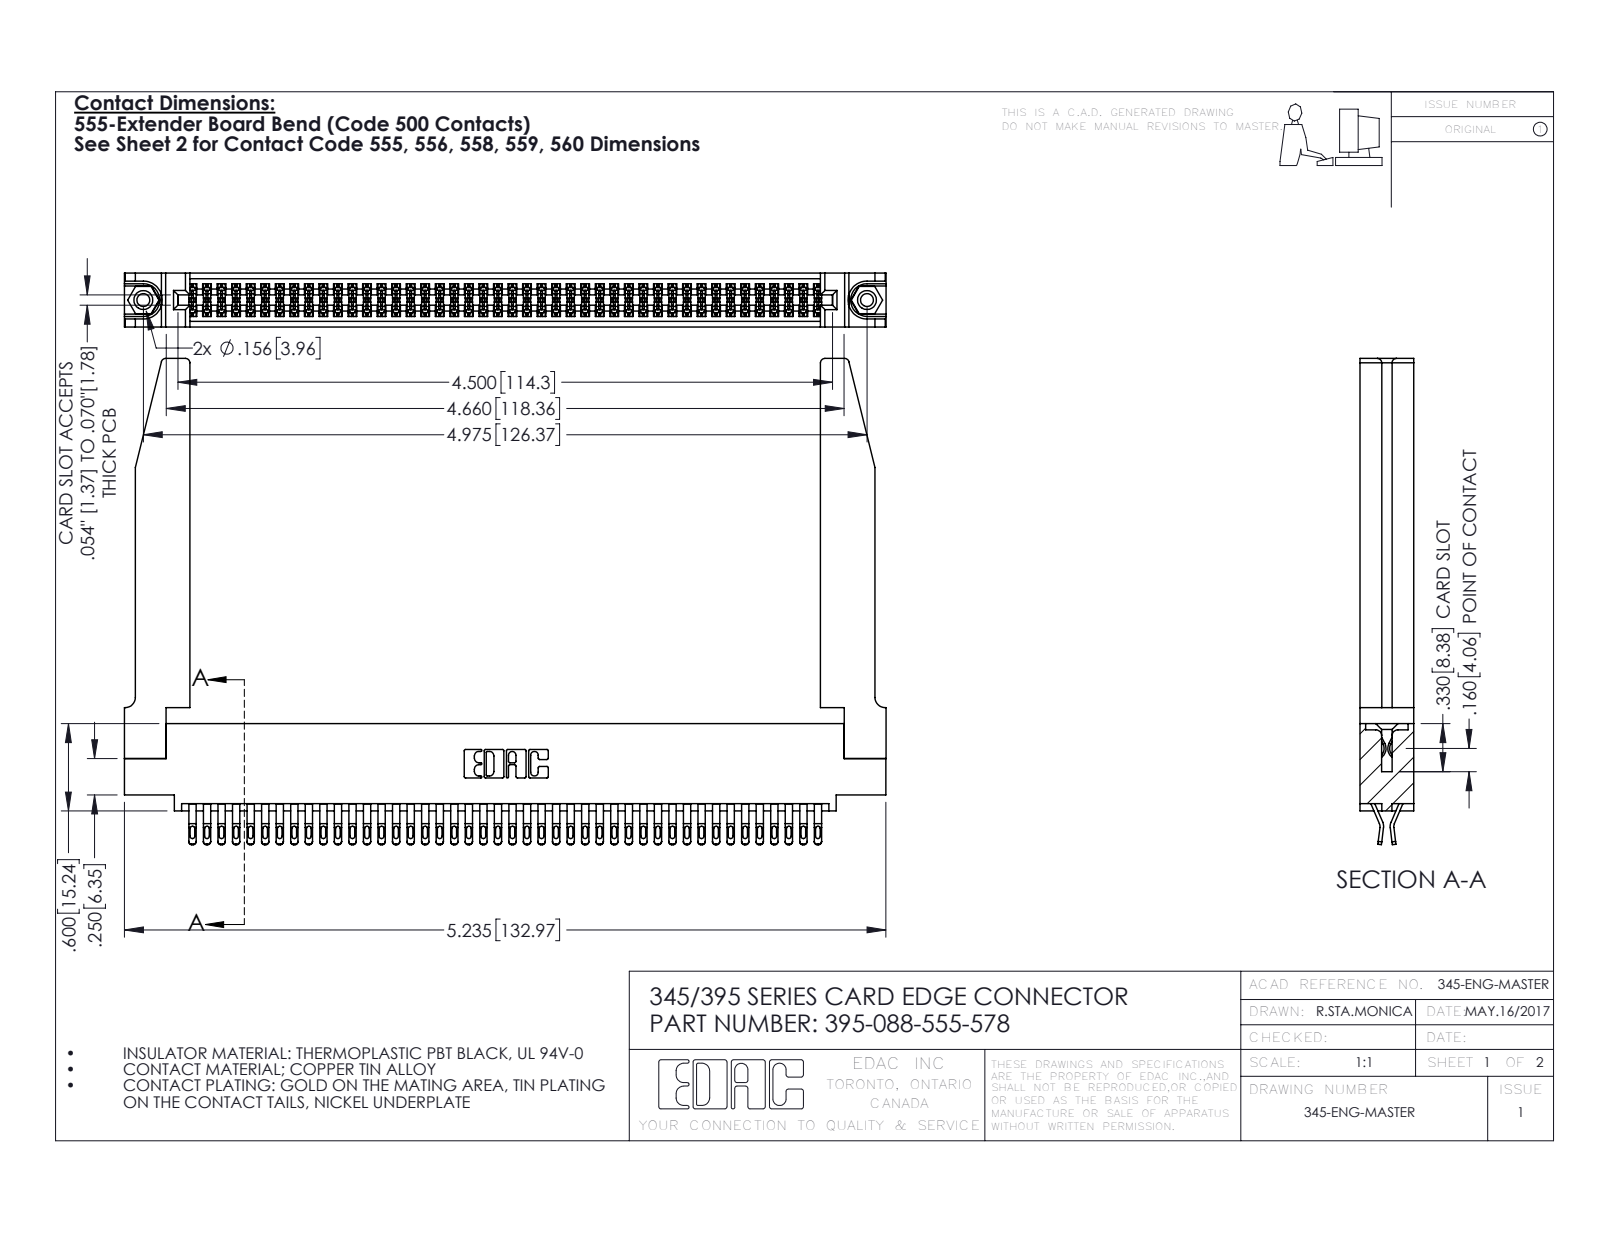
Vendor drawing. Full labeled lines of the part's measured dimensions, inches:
Part name (STEP PRODUCT): 345-250-001_345-250-001-102; 345-292-001_555 Tail; 345-220-078_345-220-078; 345 Part_0.110 Offset - 0.156 Dia-TH (+1 more)
STEP written by: SolidWorks 2016 (CONFIG_CONTROL_DESIGN)
Units: inches
Bodies: 93 solids, 5292 faces (2954 planar, 2286 cylindrical, 52 other)
Overall size (bounding box): 5.236 × 3.342 × 0.37
Volume: 1.275 in³ · Surface area: 42.24 in²
Round holes (diameter × count): ⌀0.089 ×2, ⌀0.125 ×2, ⌀0.156 ×2, ⌀0.064 ×1
Round bosses / shafts (diameter × count): ⌀0.155 ×2
Partial cylindrical surfaces — rounded edges, fillets, slot ends (radius × count): R0.016 ×220, R0.02 ×176, R0.006 ×132, R0.01 ×22, R0.03 ×8, R0.007 ×6, R0.031 ×6, R0.026 ×3
Main face-to-face distances: 0.37, 0.072, 0.298, 0.025, 0.2, 0.098, 0.272, 0.225, 0.148, 0.15
Hole centre spacings: 0.27, 4.739, 4.975
